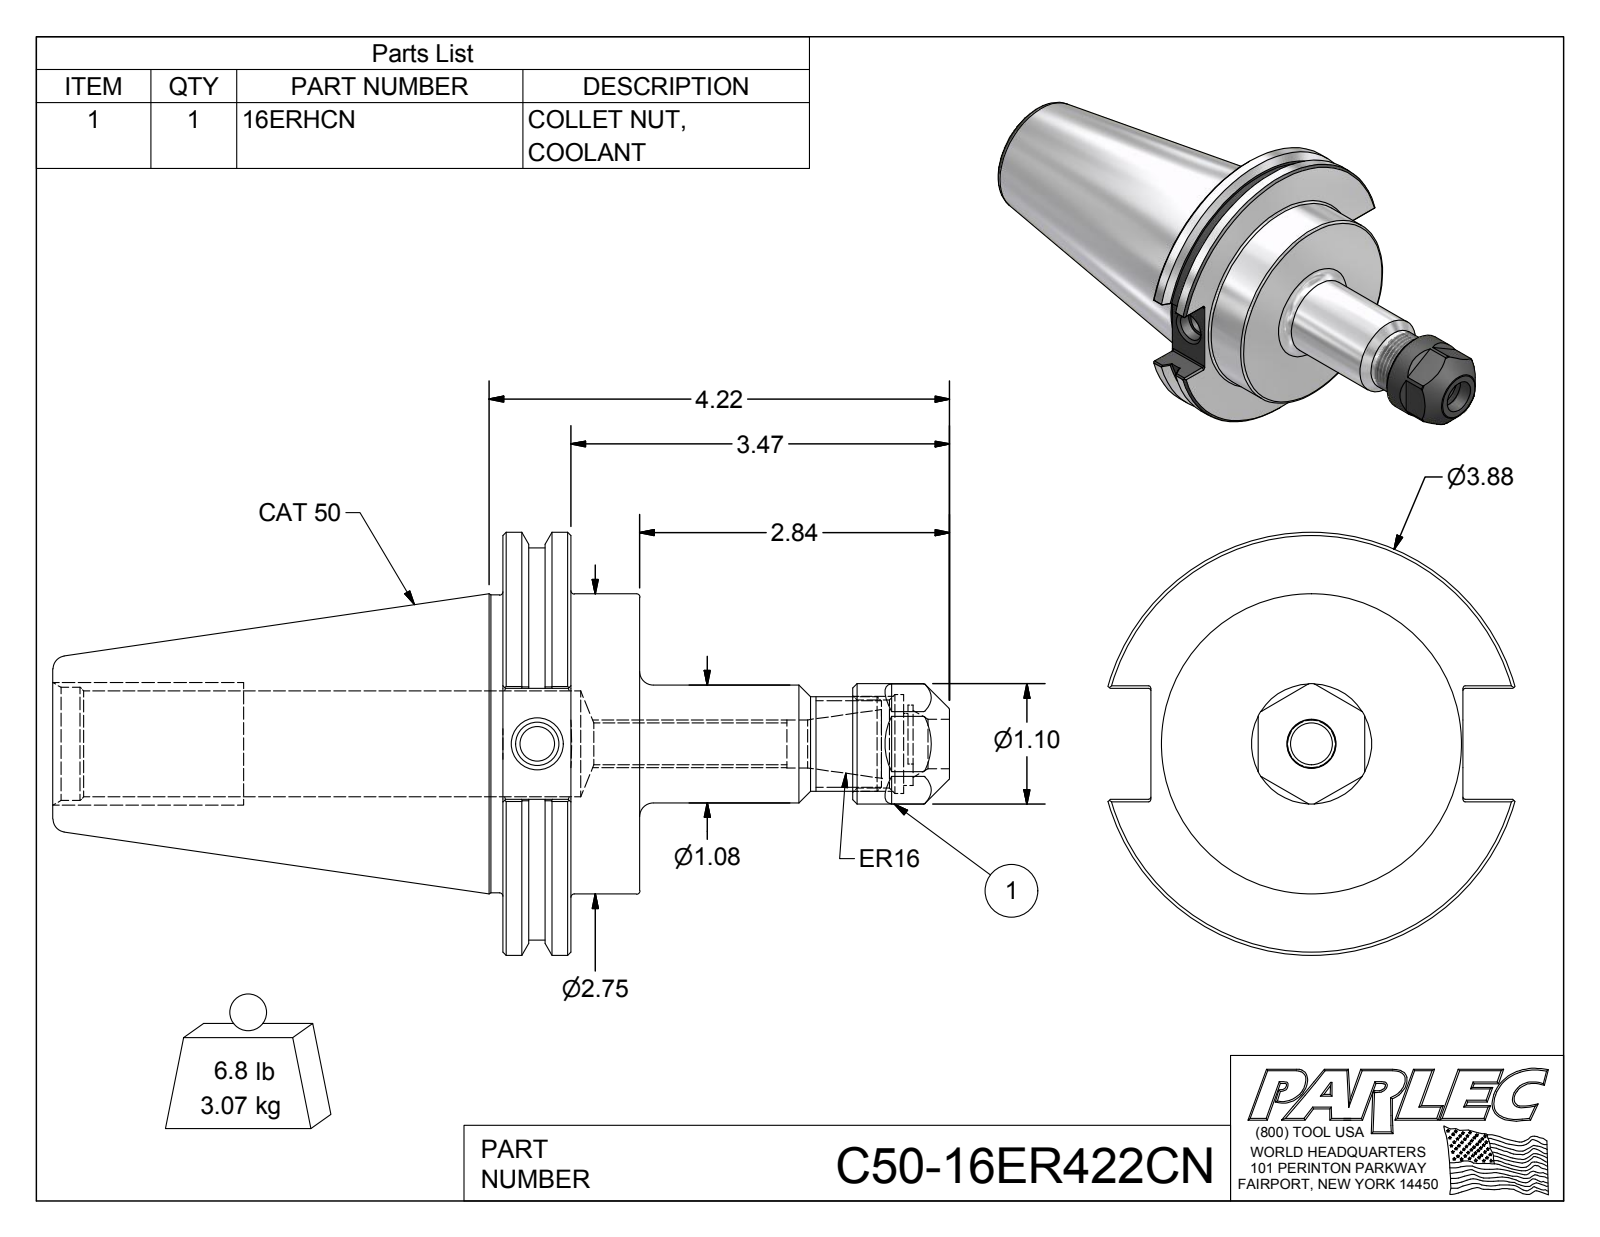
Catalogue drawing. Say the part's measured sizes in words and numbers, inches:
The part is named "C50-16ER422CN; C50-16ER4-1; 16ERHCN". Its 3-D file was written by "Autodesk Inventor 2012 (AUTOMOTIVE_DESIGN)". It is 2 solids with 128 faces: 50 planar, 34 cylindrical and 44 other. Overall it measures 8.22 by 3.875 by 3.729 inches. Its volume is 24.12 cubic inches and its surface area 92.14 square inches. Round holes: 1 of diameter 0.315, 1 of diameter 0.383, 1 of diameter 0.399, 1 of diameter 0.44, 1 of diameter 0.453, 1 of diameter 0.661, 1 of diameter 0.807, 1 of diameter 0.906, 1 of diameter 0.97, 1 of diameter 1.038. Round bosses or shafts: 1 of diameter 3.875, 1 of diameter 3.594, 1 of diameter 2.75, 1 of diameter 2.73, 1 of diameter 1.102, 1 of diameter 1.08, 1 of diameter 0.866. Partial cylindrical surfaces (rounded edges, fillets, slot ends): 12 of radius 0.02, 1 of radius 0.354. The main face-to-face distances are 1.255, 0.625, 0.63, 0.979, 4.125, 4.75, 5.38, 2.86, 1.015, 0.866. The hole center spacings are 0.051.
